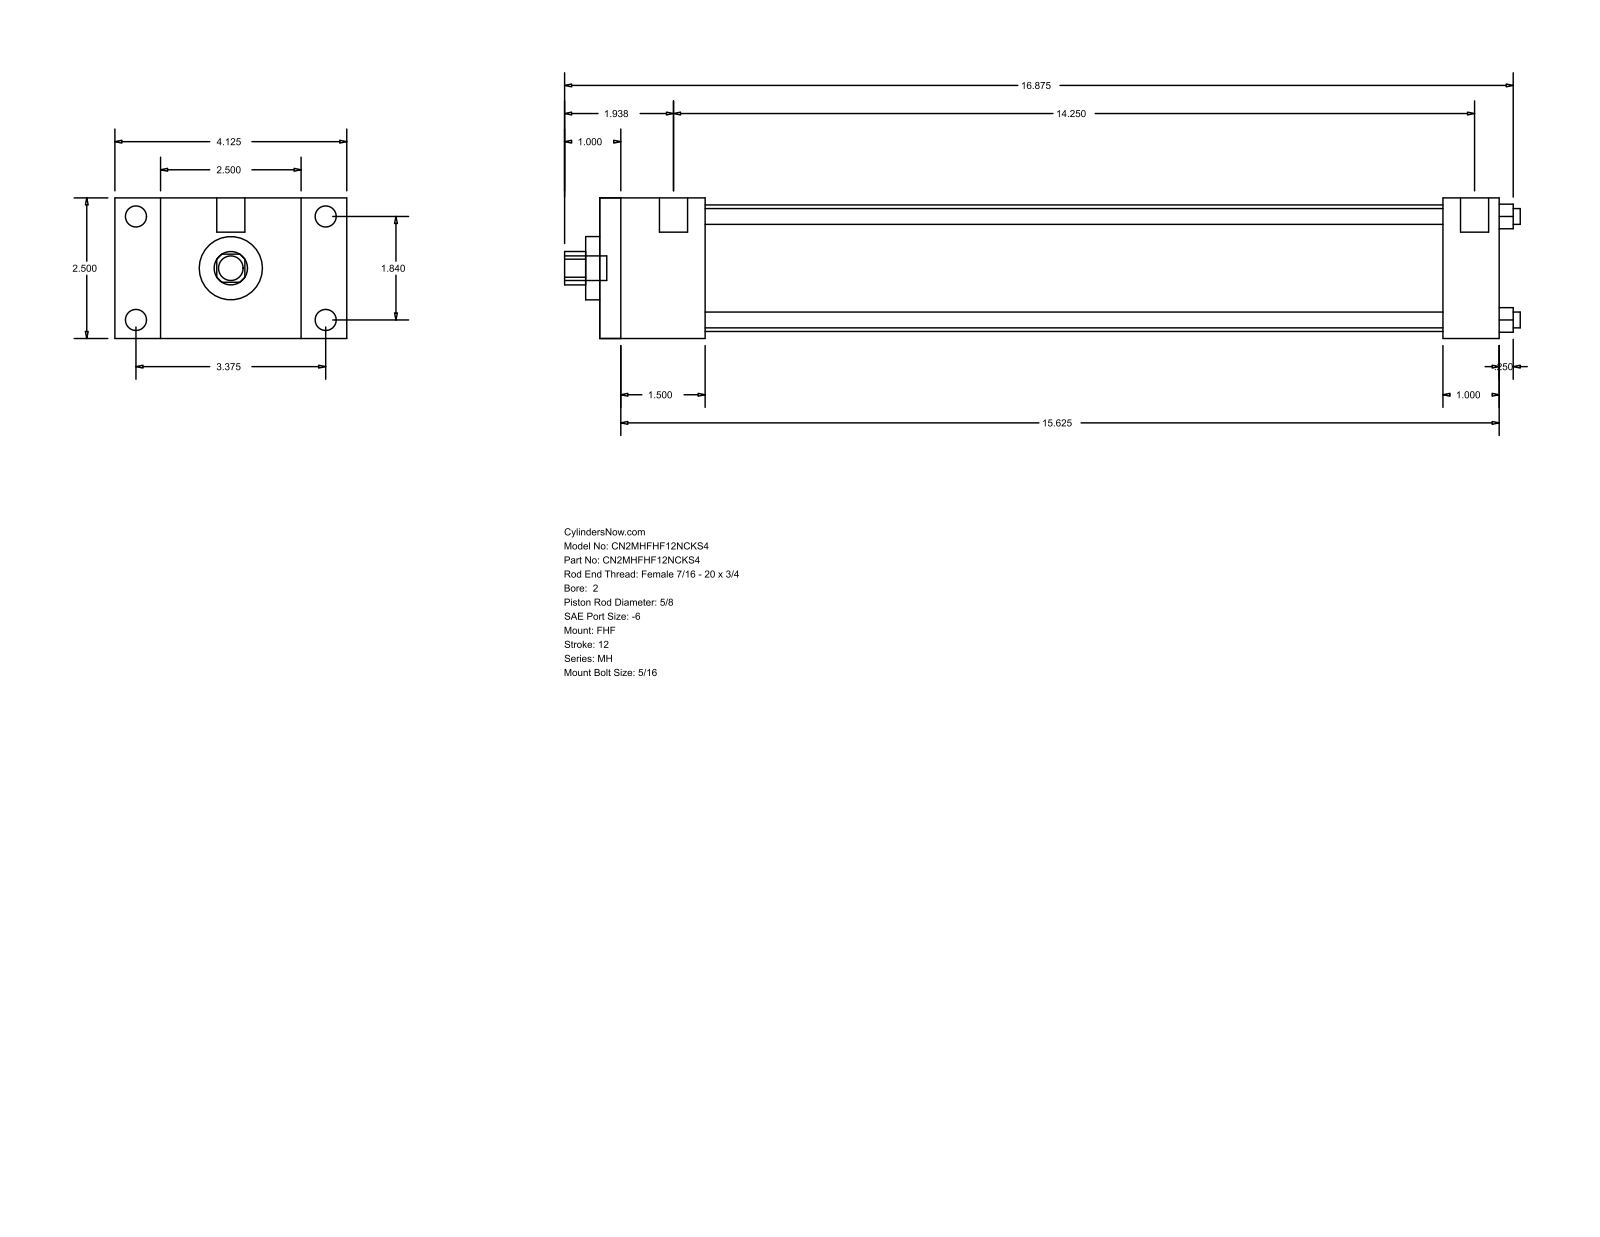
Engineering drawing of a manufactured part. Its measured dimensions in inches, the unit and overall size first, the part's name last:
Units: inches
Overall size (bounding box): 17 × 4.125 × 2.5
Round holes (diameter × count): ⌀0.281 ×4, ⌀0.625 ×1, ⌀1.125 ×1, ⌀2.25 ×1
Round bosses / shafts (diameter × count): ⌀0.375 ×4, ⌀0.219 ×4, ⌀0.5 ×2, ⌀0.437 ×1
Partial cylindrical surfaces — rounded edges, fillets, slot ends (radius × count): R0.297 ×1
Main face-to-face distances: 2.5, 1.875, 16, 14.125, 0.813, 3.313, 4.125, 15, 13.125, 1
Hole centre spacings: 1.301, 1.84, 2.602
Bodies: 0 solids, 88 faces (60 planar, 28 cylindrical, 0 other)
Part name (STEP PRODUCT): MH_FHF__0200_0.625
STEP written by: GSSL Pune (CONFIG_CONTROL_DESIGN)
